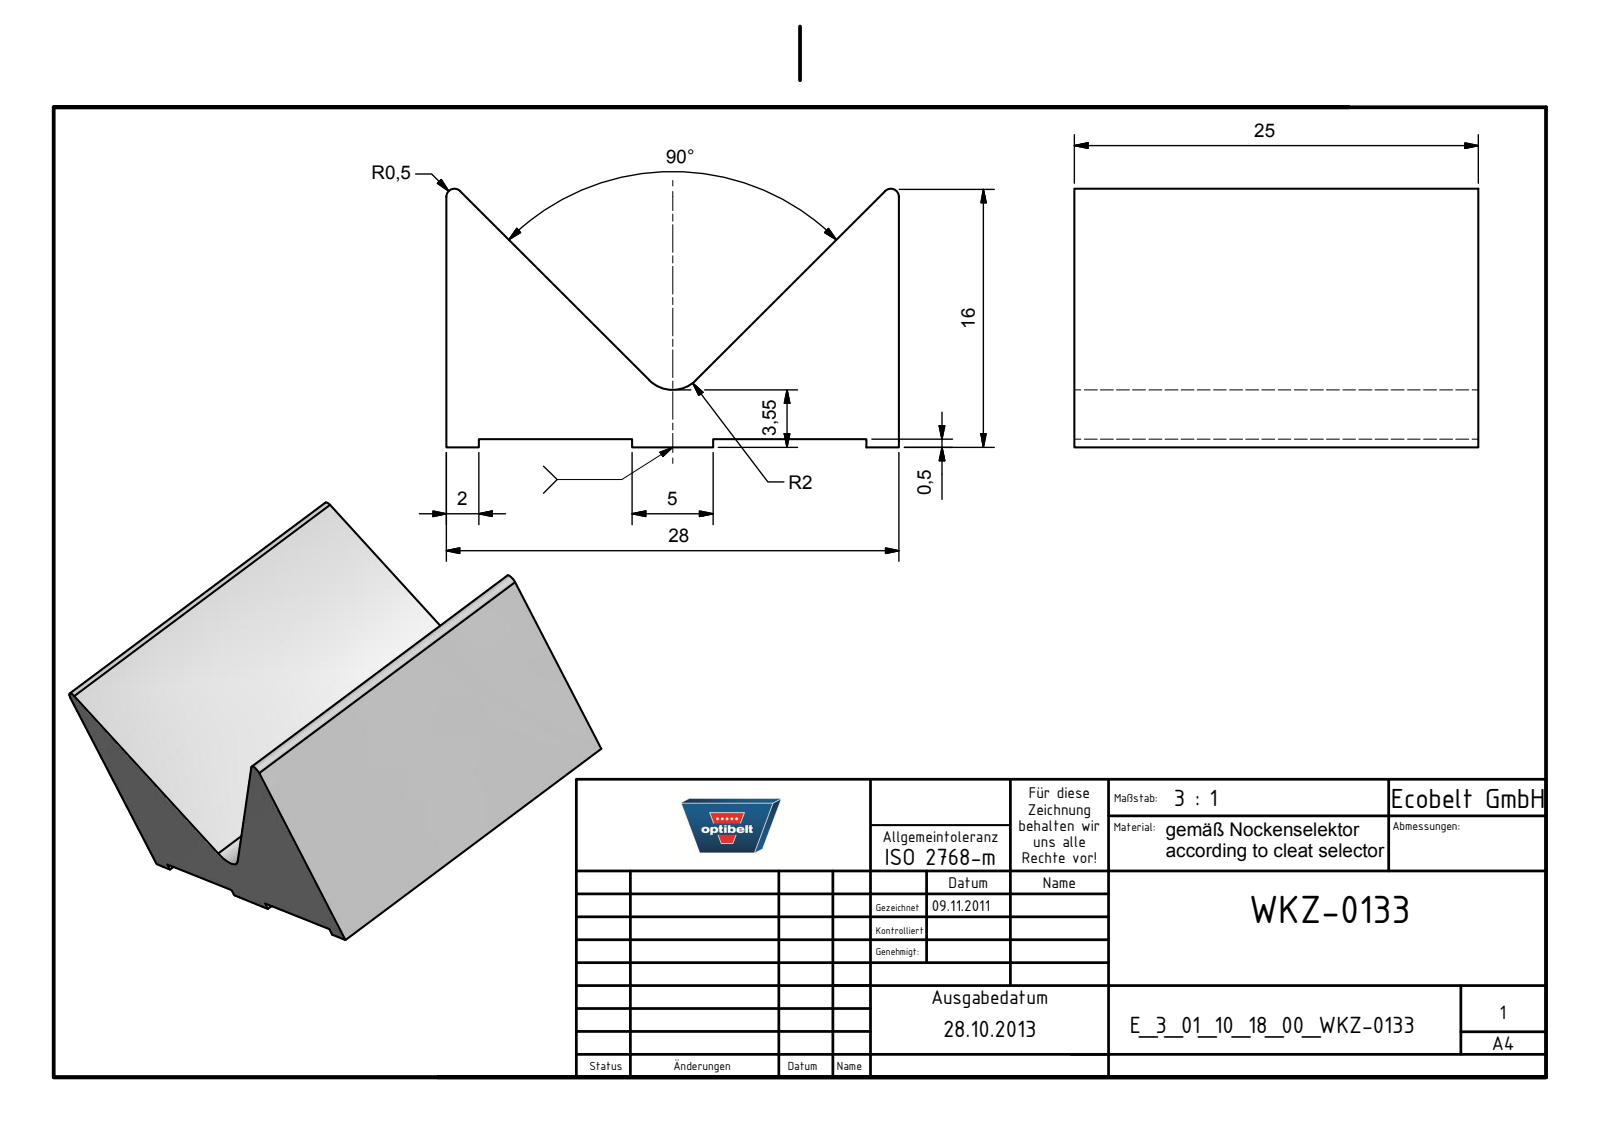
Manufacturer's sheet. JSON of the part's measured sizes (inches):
{"part_name": "E_3_01_10_18_00_WKZ-0133", "step_written_by": "Autodesk Inventor 2025 (AUTOMOTIVE_DESIGN)", "units": "inches", "bodies": {"solids": 1, "faces": 18, "planar": 15, "cylindrical": 3, "other": 0}, "overall_size": [1.102, 0.984, 0.63], "volume_in3": 0.401, "surface_area_in2": 4.676, "partial_cylinders_radius": [[0.02, 2], [0.081, 1]], "face_to_face_distances": [1.102, 0.984, 0.02, 0.453, 0.65, 0.079, 1.024, 0.374, 0.571, 0.197]}
